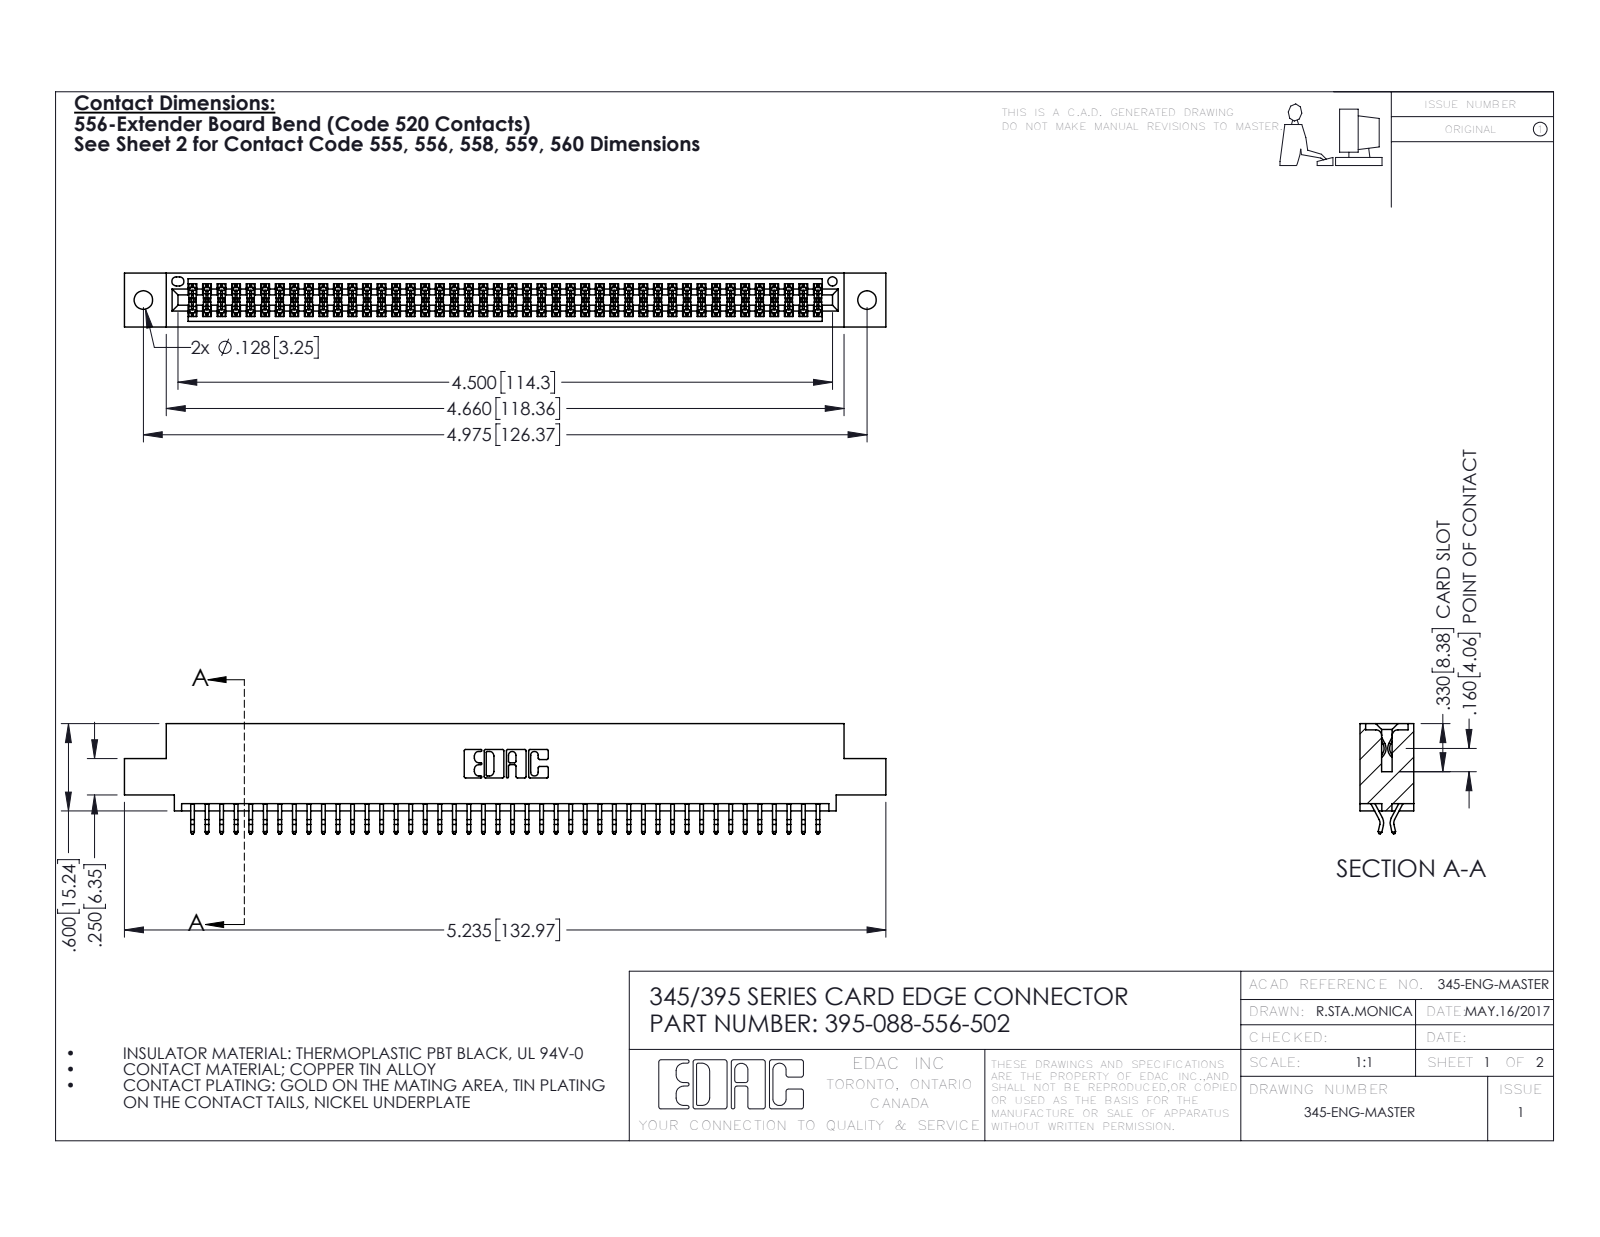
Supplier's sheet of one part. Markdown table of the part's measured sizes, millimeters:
| quantity | value |
| --- | --- |
| part name | 345-292-001_556 Tail; 395-088-556-502; 345 Part_0.110 Offset - 0.128 Dia |
| STEP written by | SolidWorks 2016 (CONFIG_CONTROL_DESIGN) |
| units | millimeters |
| bodies | 89 solids, 5058 faces (3340 planar, 1718 cylindrical, 0 other) |
| overall size | 133 × 19.2 × 9.4 |
| volume | 12 800 mm³ |
| surface area | 18 740 mm² |
| round holes (diameter × count) | 3.3 × 2, 1.6 × 1 |
| partial cylindrical surfaces (radius × count) | 0.2 × 132, 0.3 × 22, 0.2 × 6, 0.8 × 6, 0.7 × 3, 0.3 × 2, 0.4 × 2, 0.5 × 2 |
| main face-to-face distances | 7.6, 1.8, 9.4, 5.1, 0.6, 2.5, 6.9, 5.7, 4.4, 3.8 |
| hole center spacings | 6.9, 120.4, 126.4 |
